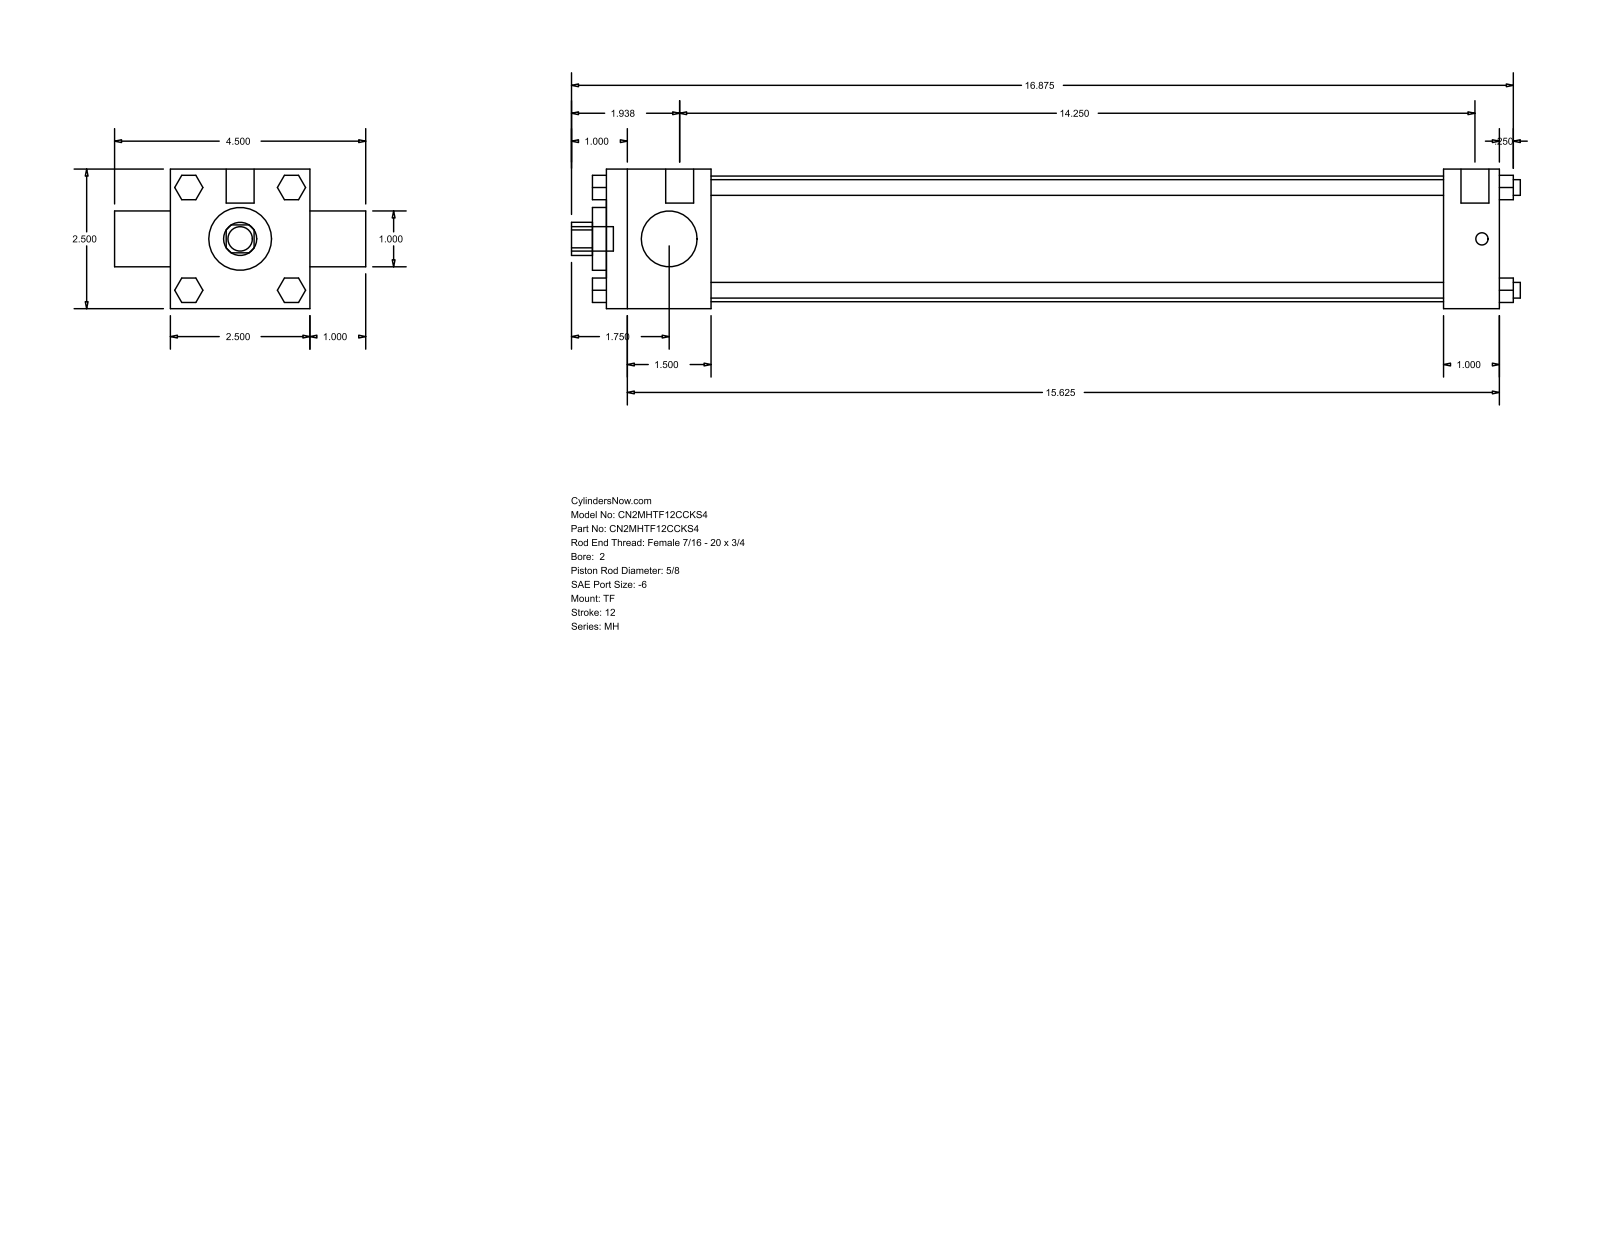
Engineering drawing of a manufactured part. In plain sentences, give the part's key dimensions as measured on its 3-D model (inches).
The part is named "MH_TF__0200_0.625". Its 3-D file was written by "GSSL Pune (CONFIG_CONTROL_DESIGN)". It is 0 solids with 120 faces: 92 planar, 28 cylindrical and 0 other. Overall it measures 17 by 4.5 by 2.5 inches. Round holes: 1 of diameter 0.625, 1 of diameter 1, 1 of diameter 1.125, 1 of diameter 2.25. Round bosses or shafts: 4 of diameter 0.281, 3 of diameter 0.219, 2 of diameter 0.5, 1 of diameter 0.437. Partial cylindrical surfaces (rounded edges, fillets, slot ends): 1 of radius 0.297. The main face-to-face distances are 2.5, 16, 1.875, 15, 13.125, 14.125, 1, 1, 0.25, 3.5.
